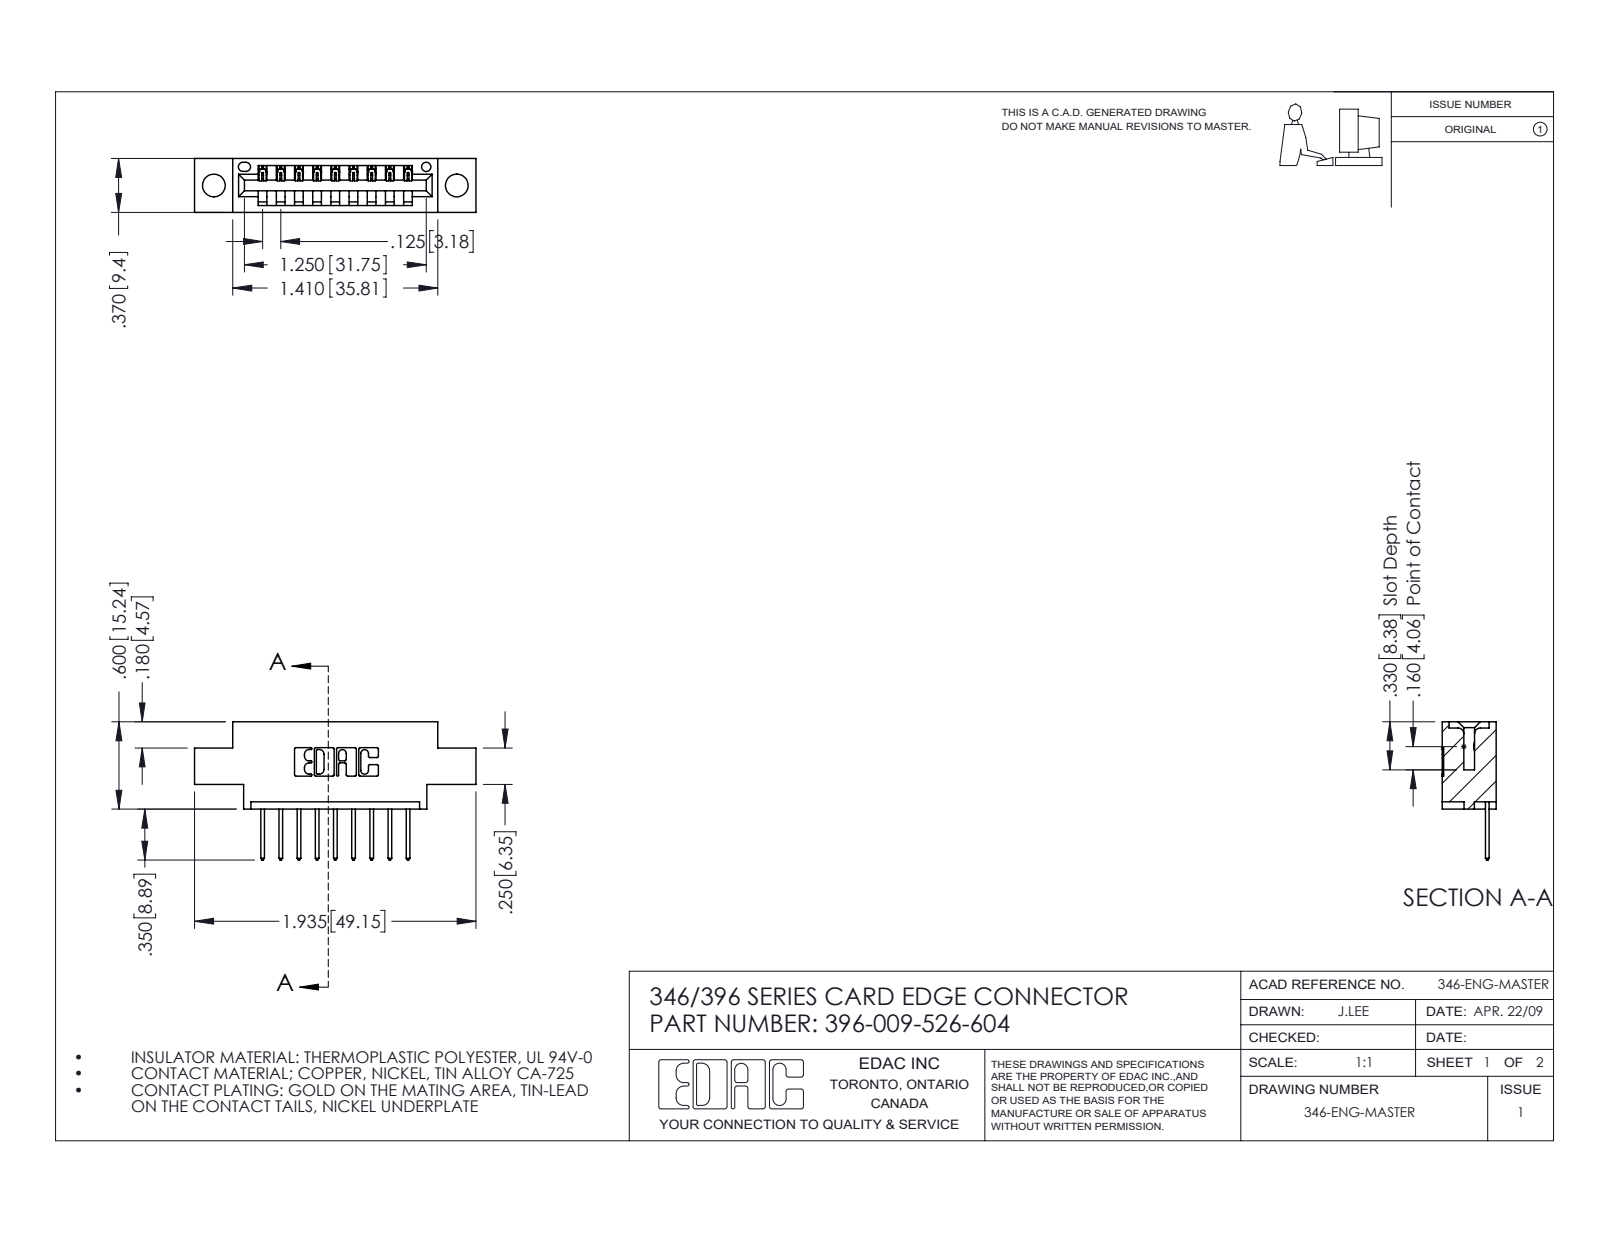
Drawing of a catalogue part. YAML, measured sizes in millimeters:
part_name: "346 Part_0.170 Offset - 0.156 Dia-TH; 396-009-526-604; 345-292-001_345-293-126"
step_written_by: "SolidWorks 2016 (CONFIG_CONTROL_DESIGN)"
units: millimeters
bodies: {solids: 10, faces: 648, planar: 440, cylindrical: 208, other: 0}
overall_size: [49.1, 24.1, 9.4]
volume: 4230
surface_area: 4885
round_holes:
  - {diameter: 4, count: 2}
  - {diameter: 1.6, count: 1}
partial_cylinders:
  - {radius: 0.3, count: 22}
  - {radius: 0.2, count: 18}
  - {radius: 0.3, count: 18}
  - {radius: 0.2, count: 6}
  - {radius: 0.8, count: 6}
  - {radius: 0.7, count: 3}
  - {radius: 0.8, count: 2}
  - {radius: 1, count: 2}
face_to_face_distances: [6.4, 9.4, 1.2, 8.2, 1.8, 7.6, 0.6, 3.8, 5.6, 2.5]
hole_center_spacings: [6.2, 37.2, 42.4]
